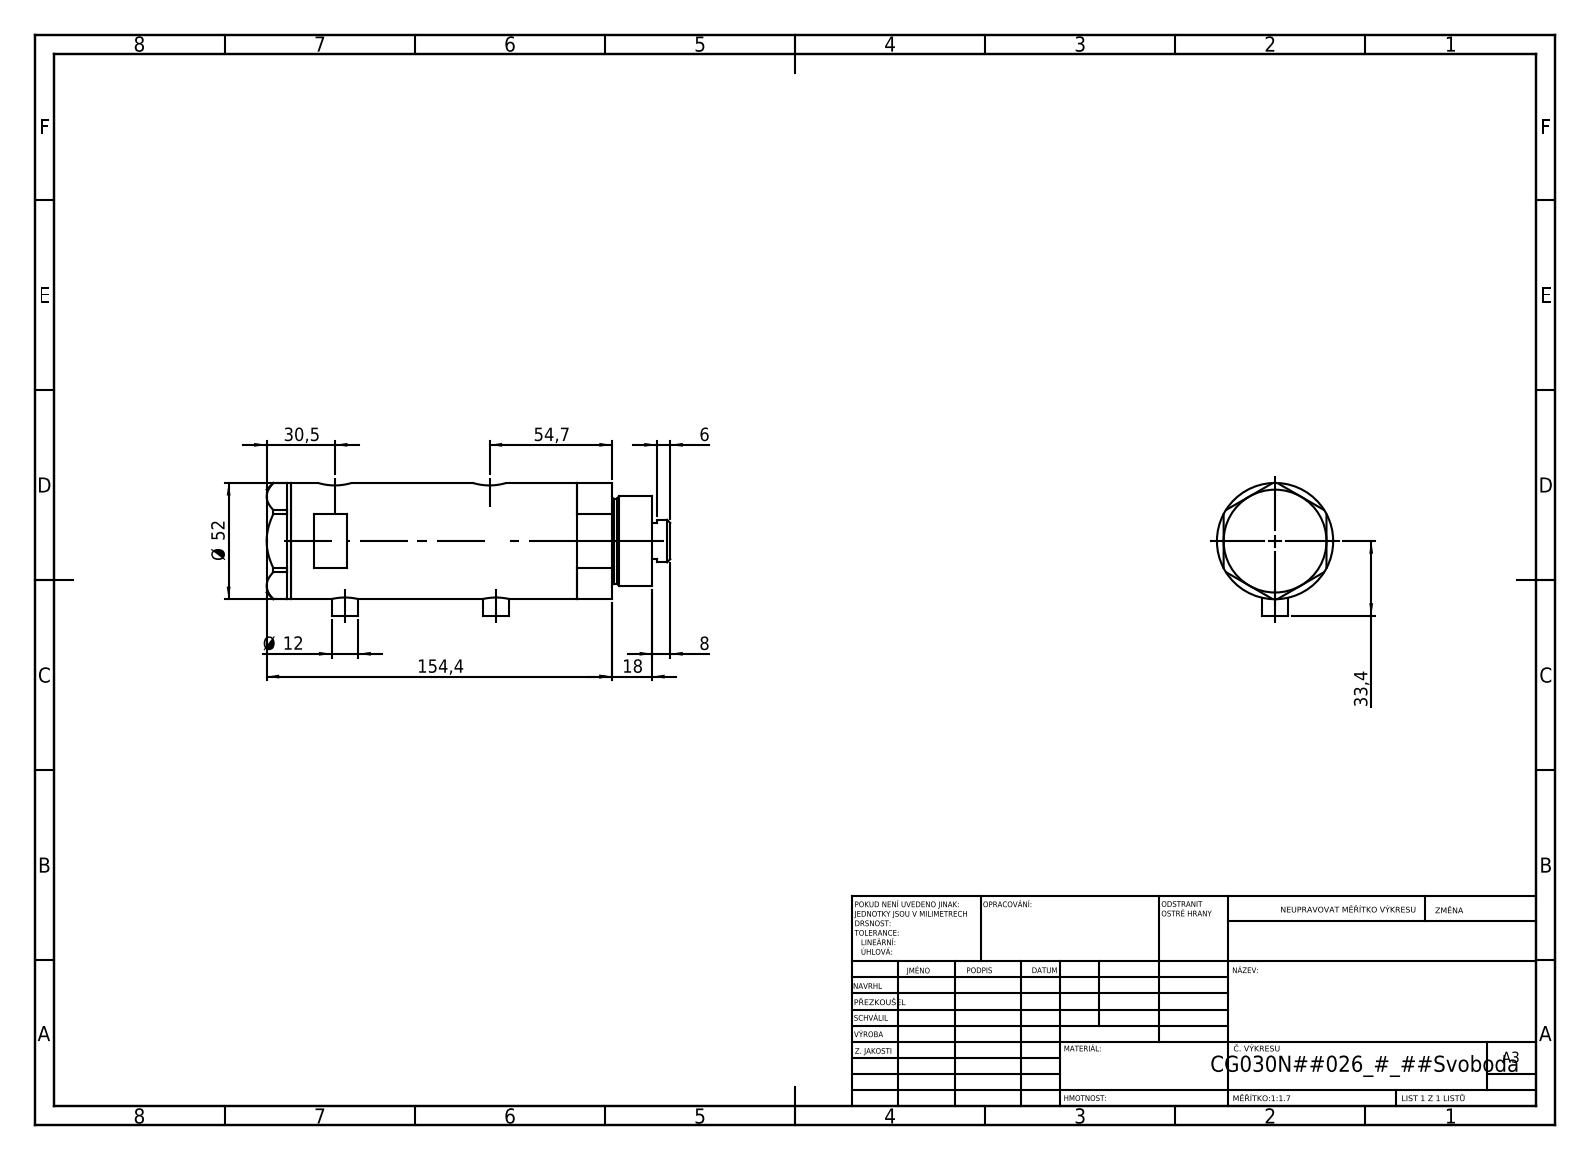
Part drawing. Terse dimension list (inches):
name: V270CG_MIDDLE; V270CG_BACK; V270CG_FRONT; V270CG_VC
written by: SolidWorks 2019 (CONFIG_CONTROL_DESIGN)
unit: in
bodies: 4 solids, 140 faces (67 planar, 53 cylindrical, 20 other)
size: 7.106 × 2.339 × 2.047
volume: 20.23 in³; area: 119.6 in²
holes: 2× ⌀0.197, 2× ⌀0.383, 2× ⌀0.492, 2× ⌀0.591, 1× ⌀0.256, 1× ⌀0.787, 1× ⌀0.846, 1× ⌀1.181, 1× ⌀1.299, 1× ⌀1.732
bosses: 2× ⌀0.472, 1× ⌀2.047, 1× ⌀1.575, 1× ⌀1.496, 1× ⌀0.748
face distances: 3.602, 0.937, 2.665, 0.433, 1.37, 4.035, 1.811, 5.469, 5.035, 4.098
hole spacings: 0.114, 0.177, 2.547, 2.661, 2.724, 2.839
